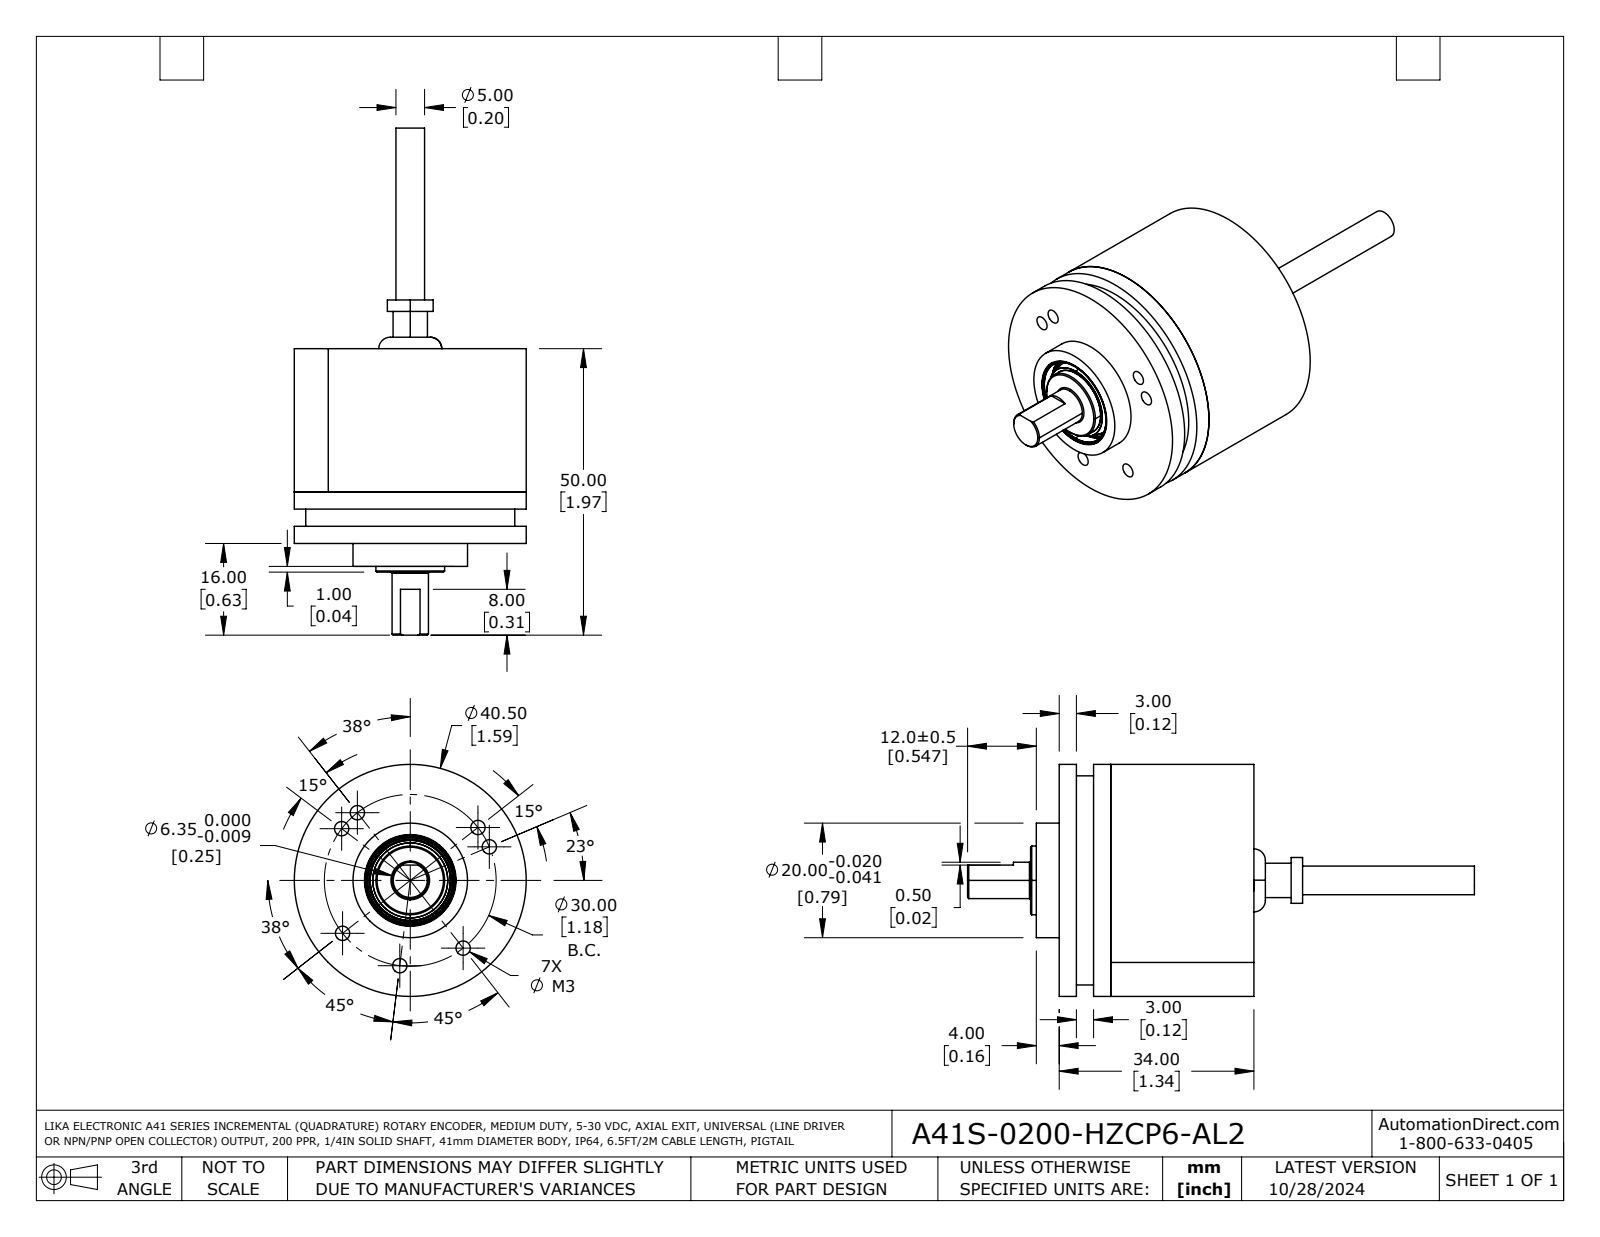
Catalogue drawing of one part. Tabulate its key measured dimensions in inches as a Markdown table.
| quantity | value |
| --- | --- |
| part name | A41S-0200-HZCP6-AL2 |
| STEP written by | SolidWorks 2021 (AUTOMOTIVE_DESIGN) |
| units | inches |
| bodies | 11 solids, 422 faces (76 planar, 145 cylindrical, 201 other) |
| overall size | 3.484 × 1.594 × 1.594 |
| volume | 1.175 in³ |
| surface area | 28.29 in² |
| round holes (diameter × count) | 0.063 × 7, 0.098 × 7, 0.157 × 3, 0.087 × 2, 0.169 × 1, 0.295 × 1, 0.512 × 1, 0.602 × 1, 0.612 × 1, 0.63 × 1, 1.516 × 1 |
| round bosses / shafts (diameter × count) | 0.079 × 2, 1.594 × 1, 1.496 × 1, 1.457 × 1, 1.437 × 1, 0.787 × 1, 0.472 × 1, 0.315 × 1 |
| partial cylindrical surfaces (radius × count) | 0.039 × 14, 0.007 × 6, 0.008 × 2 |
| main face-to-face distances | 0.118, 1.339, 0.433, 0.906, 1.22, 0.079, 0.866, 0.984, 0.787, 0.039 |
| hole center spacings | 0.591, 0.669, 0.835, 0.11, 0.118, 0.837, 0.945, 1.257 |
